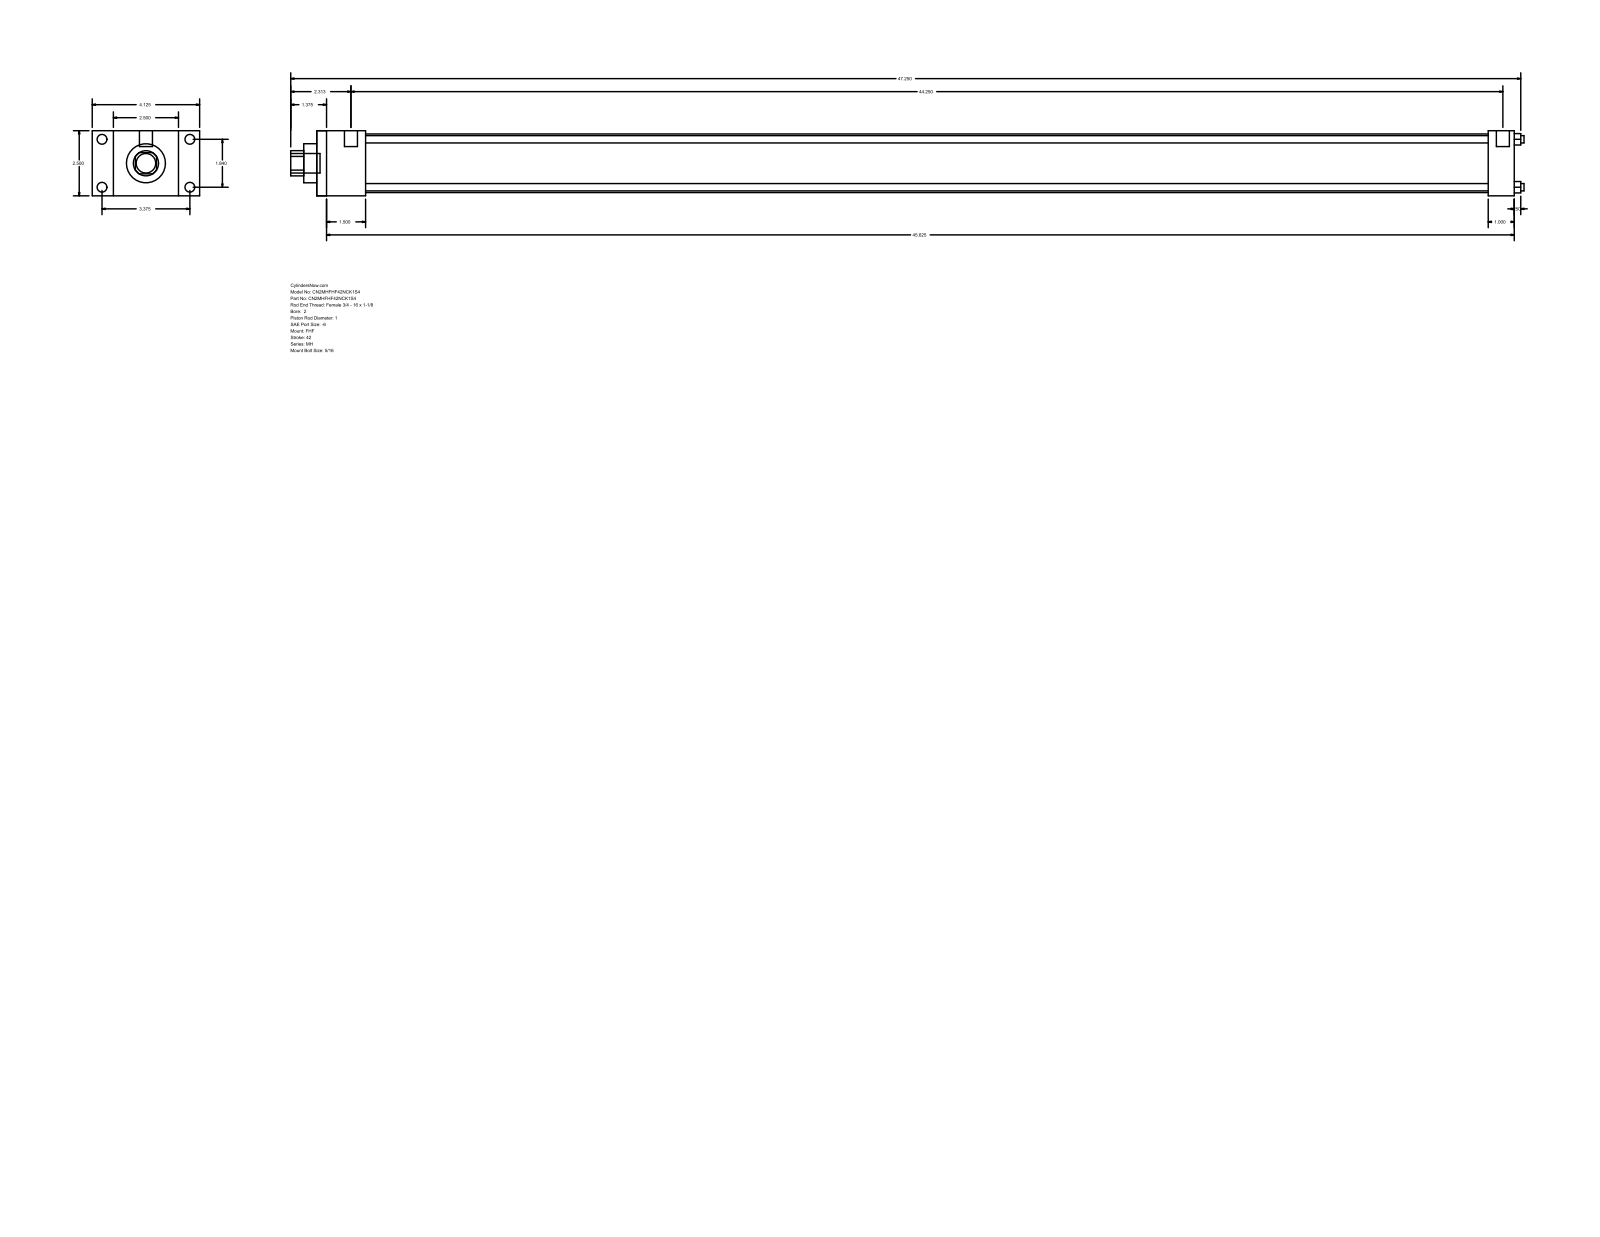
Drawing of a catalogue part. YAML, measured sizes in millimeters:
part_name: "MH_FHF__0200_1"
step_written_by: "GSSL Pune (CONFIG_CONTROL_DESIGN)"
units: millimeters
bodies: {solids: 0, faces: 88, planar: 60, cylindrical: 28, other: 0}
overall_size: [1203.33, 104.78, 63.5]
round_holes:
  - {diameter: 7.14, count: 4}
  - {diameter: 25.4, count: 1}
  - {diameter: 38.1, count: 1}
  - {diameter: 57.15, count: 1}
round_bosses_or_shafts:
  - {diameter: 9.53, count: 4}
  - {diameter: 5.56, count: 4}
  - {diameter: 12.7, count: 2}
  - {diameter: 19.05, count: 1}
partial_cylinders:
  - {radius: 12.29, count: 1}
face_to_face_distances: [63.5, 1168.4, 47.63, 1120.77, 20.64, 84.14, 104.78, 25.4, 1143, 1095.37]
hole_center_spacings: [33.05, 46.74, 66.1]
